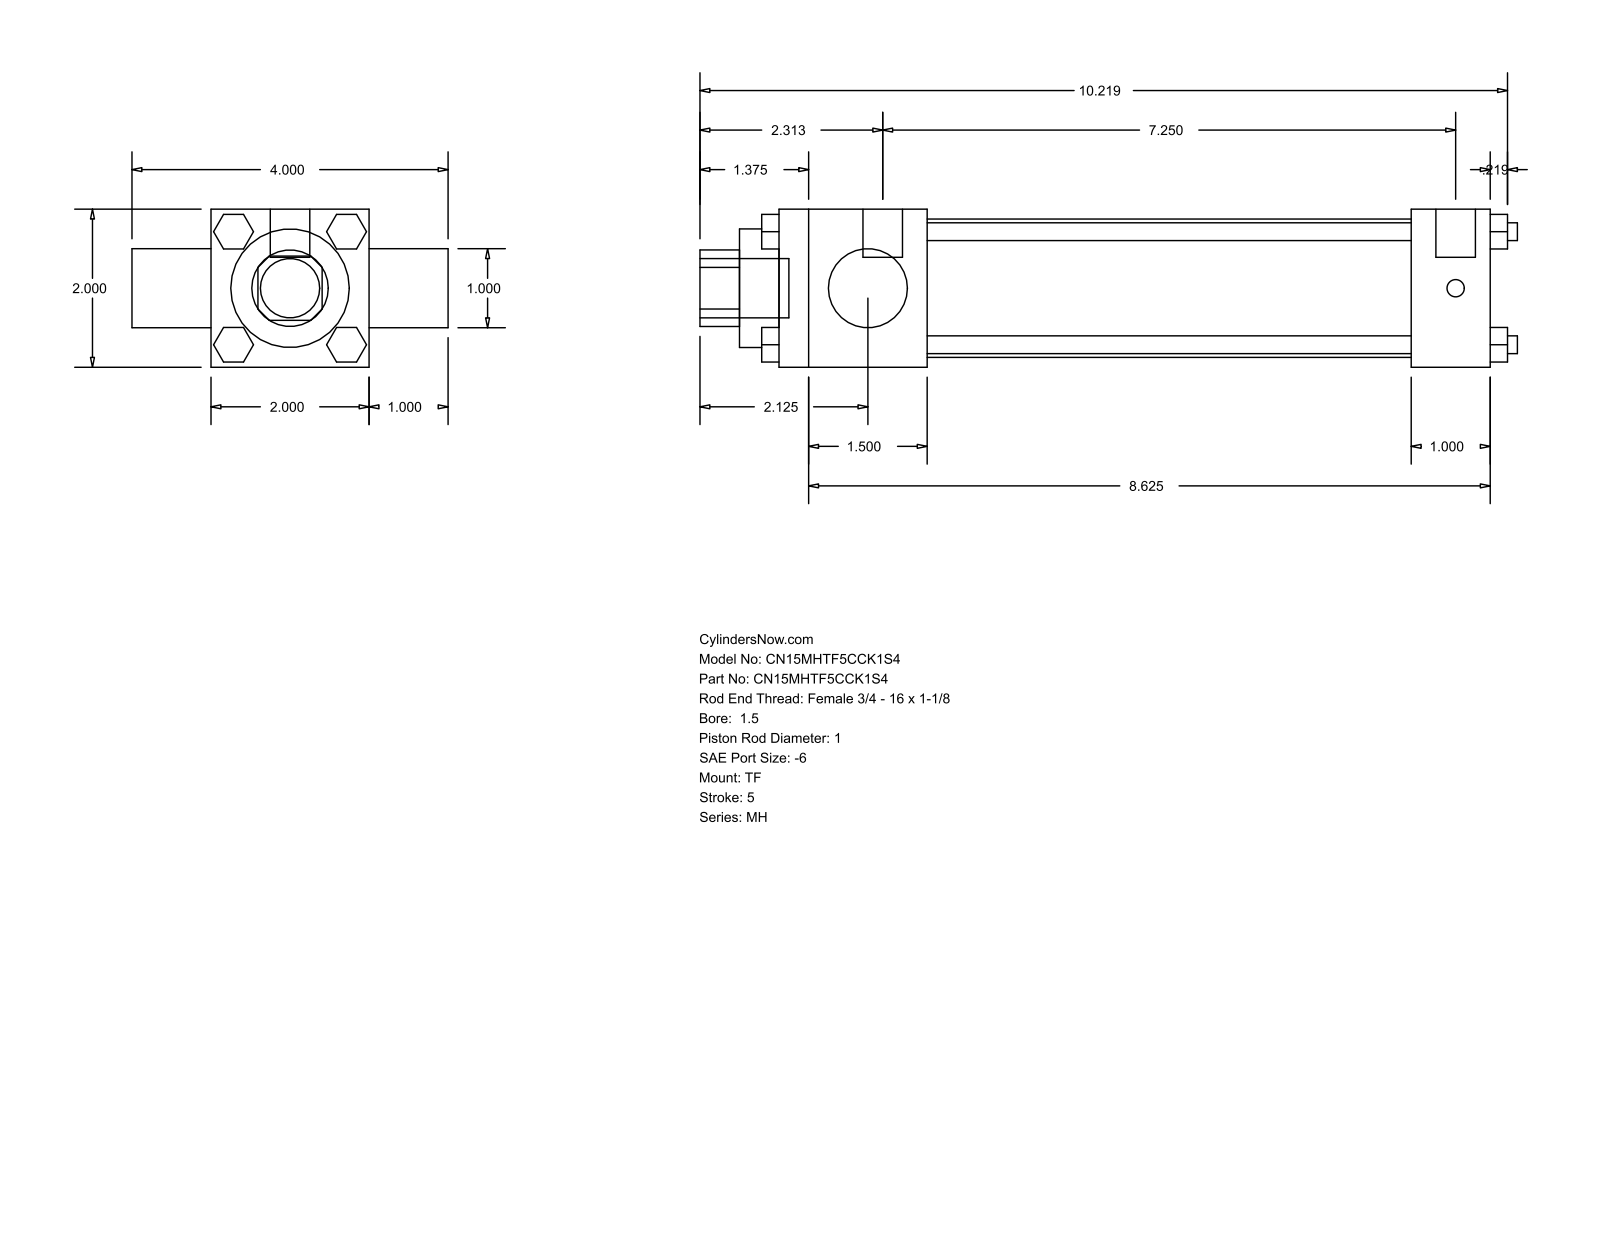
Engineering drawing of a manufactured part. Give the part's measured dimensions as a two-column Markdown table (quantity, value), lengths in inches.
| quantity | value |
| --- | --- |
| part name | MH_TF__0150_1 |
| STEP written by | GSSL Pune (CONFIG_CONTROL_DESIGN) |
| units | inches |
| bodies | 0 solids, 120 faces (92 planar, 28 cylindrical, 0 other) |
| overall size | 10.344 × 4 × 2 |
| round holes (diameter × count) | 1 × 2, 1.5 × 1, 1.75 × 1 |
| round bosses / shafts (diameter × count) | 0.225 × 4, 0.219 × 3, 0.5 × 2, 0.75 × 1 |
| partial cylindrical surfaces (radius × count) | 0.484 × 1 |
| main face-to-face distances | 2, 1, 9, 3, 1.875, 7.125, 8, 6.125, 9.219, 0.5 |
